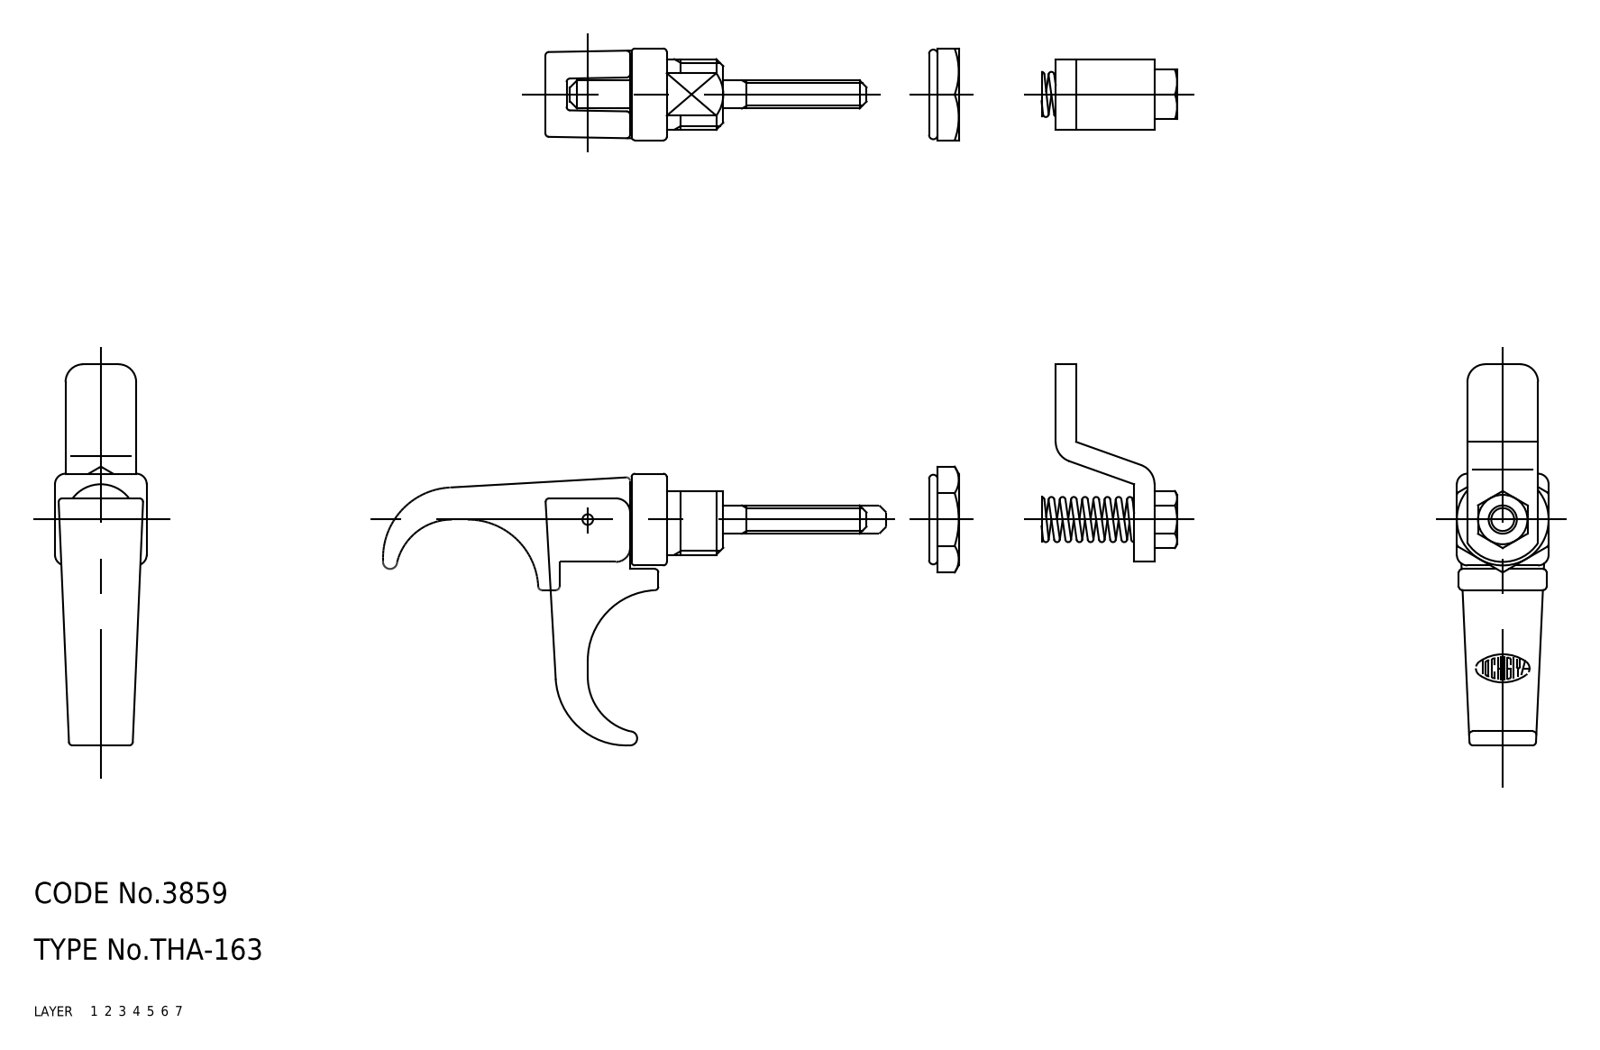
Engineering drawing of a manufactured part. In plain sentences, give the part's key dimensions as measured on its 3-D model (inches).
The part is named "spring; handle; nut_2; nut_1 (+4 more)". Its 3-D file was written by "CADfix (AUTOMOTIVE_DESIGN)". It is 8 solids with 194 faces: 0 planar, 0 cylindrical and 194 other. Overall it measures 2.126 by 1.79 by 0.512 inches. Its volume is 0.348 cubic inches and its surface area 8.22 square inches.
